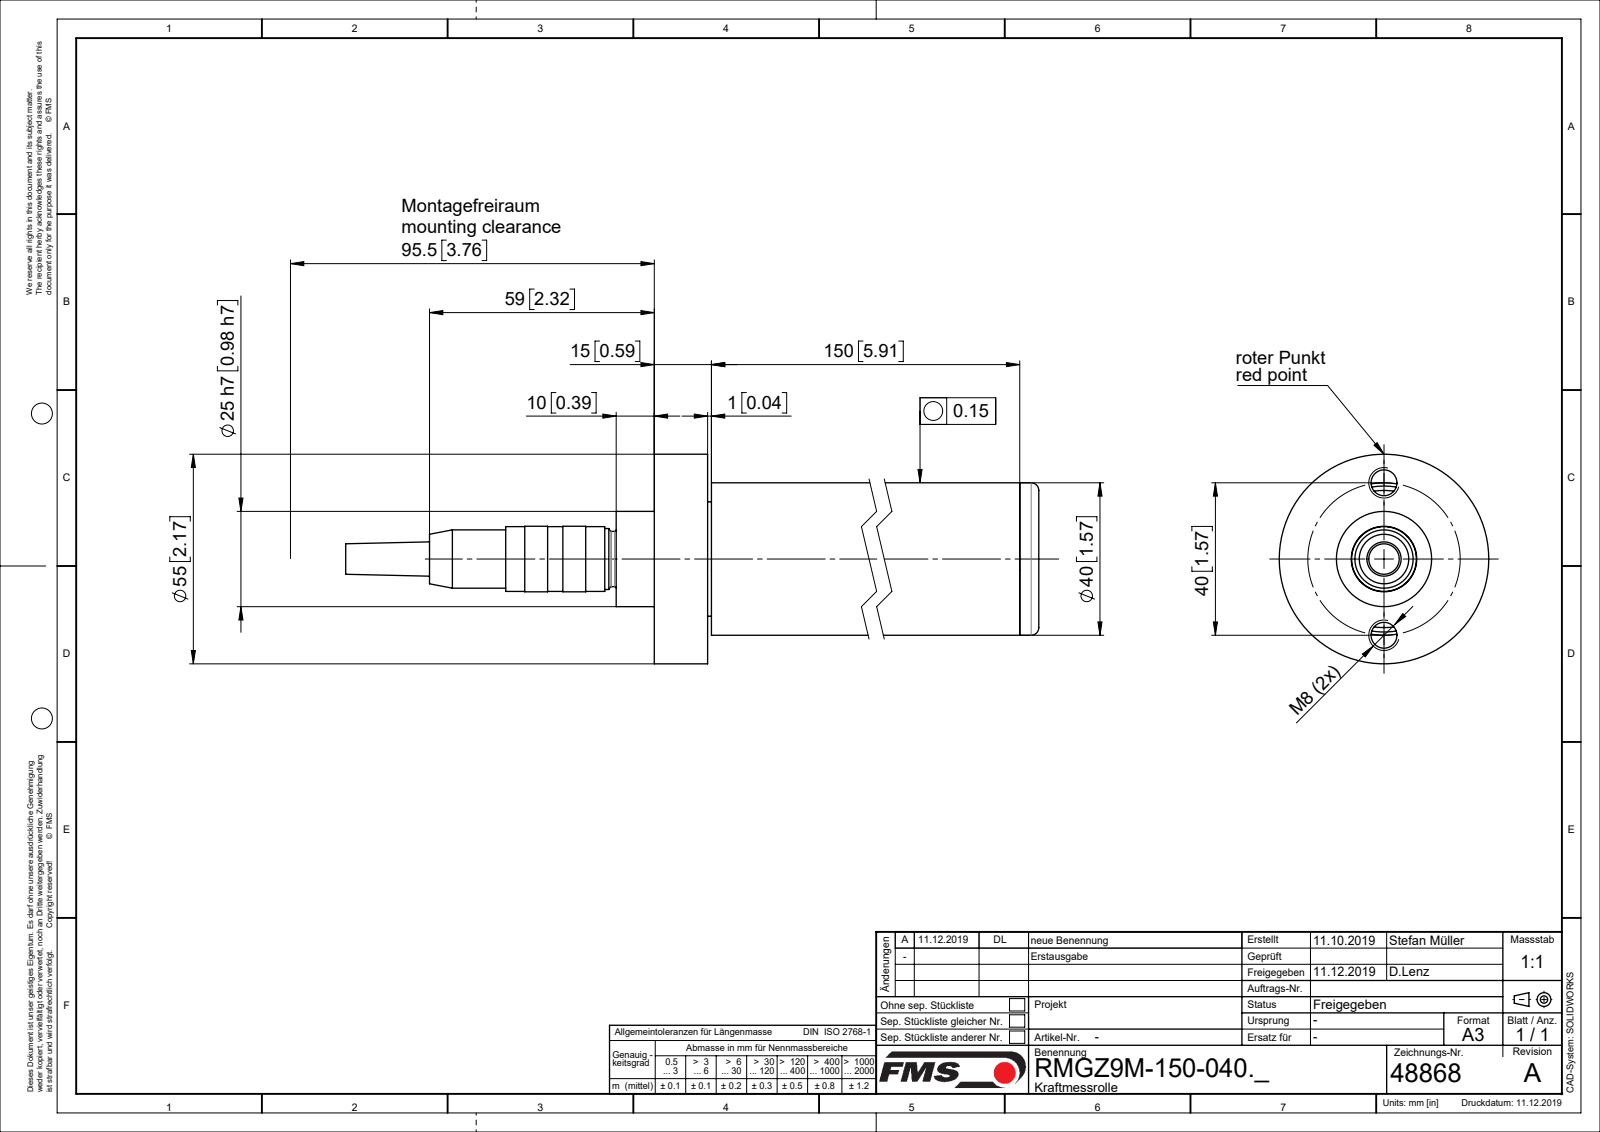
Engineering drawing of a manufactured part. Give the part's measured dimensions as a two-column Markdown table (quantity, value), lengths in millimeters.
| quantity | value |
| --- | --- |
| part name | R48868; R4862004; TEIL1; RILLENKUGELLAGER_6201 (+4 more) |
| STEP written by | Mechanical Desktop 2007 (CONFIG_CONTROL_DESIGN) |
| units | millimeters |
| bodies | 7 solids, 225 faces (63 planar, 100 cylindrical, 62 other) |
| overall size | 251 × 55 × 55 |
| volume | 140 774 mm³ |
| surface area | 72 718 mm² |
| round holes (diameter × count) | 6.91 × 2, 10 × 1, 11.5 × 1, 12 × 1, 13.3 × 1, 14 × 1, 26.3 × 1, 27 × 1, 28 × 1, 32 × 1, 36 × 1 |
| round bosses / shafts (diameter × count) | 55 × 1, 40 × 1, 31.3 × 1, 25 × 1, 17.5 × 1, 17.2 × 1, 17 × 1, 16 × 1 |
| partial cylindrical surfaces (radius × count) | 10.5 × 1 |
| main face-to-face distances | 14, 16, 7.4, 2.6, 14.5, 4.5, 169.5, 155.5, 30, 10 |
| hole center spacings | 20, 40 |
